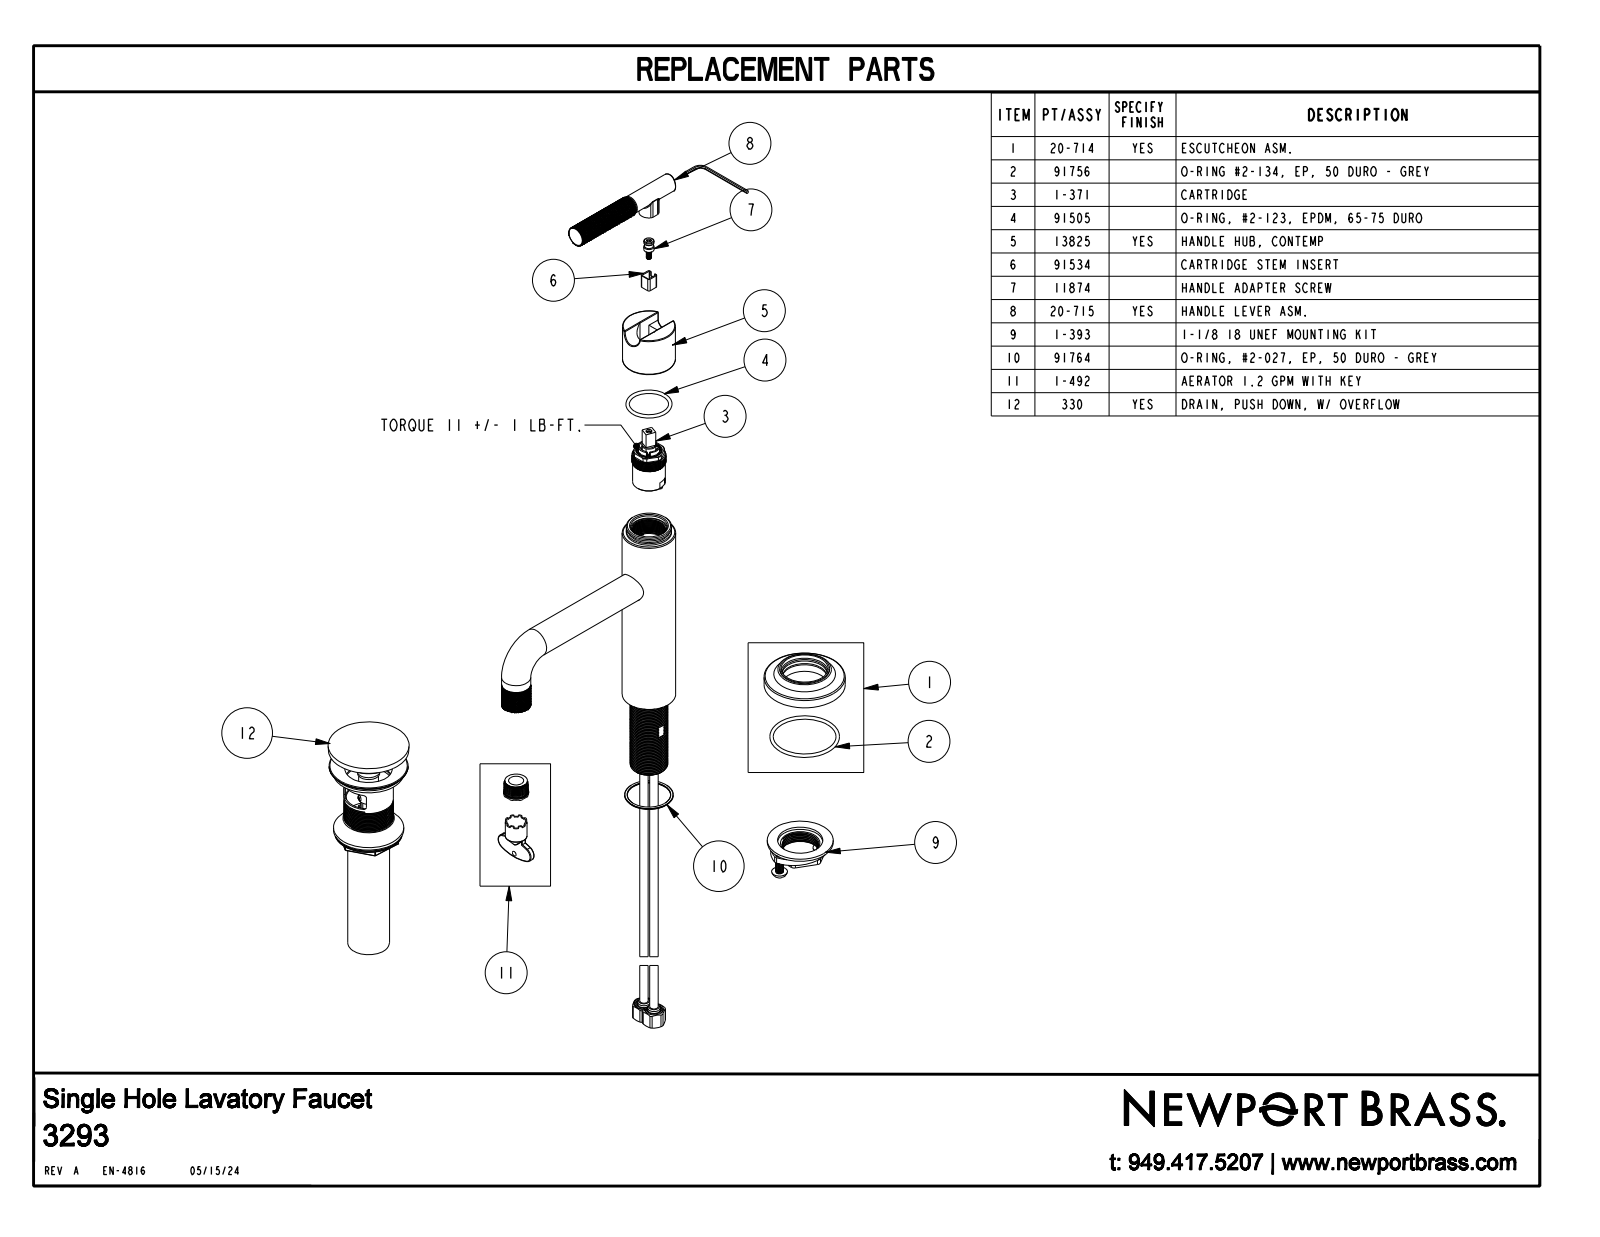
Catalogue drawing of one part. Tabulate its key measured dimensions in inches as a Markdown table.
| quantity | value |
| --- | --- |
| part name | 3293_SW0001 |
| STEP written by | CREO PARAMETRIC BY PTC INC, 2023134 (CONFIG_CONTROL_DESIGN) |
| units | inches |
| bodies | 1 solid, 12034 faces (15 planar, 2439 cylindrical, 9580 other) |
| overall size | 8.032 × 7.268 × 2.43 |
| volume | 20.91 in³ |
| surface area | 77.2 in² |
| round holes (diameter × count) | 0.88 × 1 |
| round bosses / shafts (diameter × count) | 0.875 × 2, 2.43 × 1, 1.6 × 1, 1.58 × 1, 1.51 × 1, 0.6 × 1, 0.56 × 1, 0.5 × 1 |
| partial cylindrical surfaces (radius × count) | 0.02 × 6, 0.12 × 4, 0.313 × 4, 0.06 × 2, 0.297 × 1, 0.9 × 1 |
| main face-to-face distances | 7.743, 2.97, 4.773, 0.625, 7.124, 4.154, 0.619, 0.046, 0.58, 0.534 |
